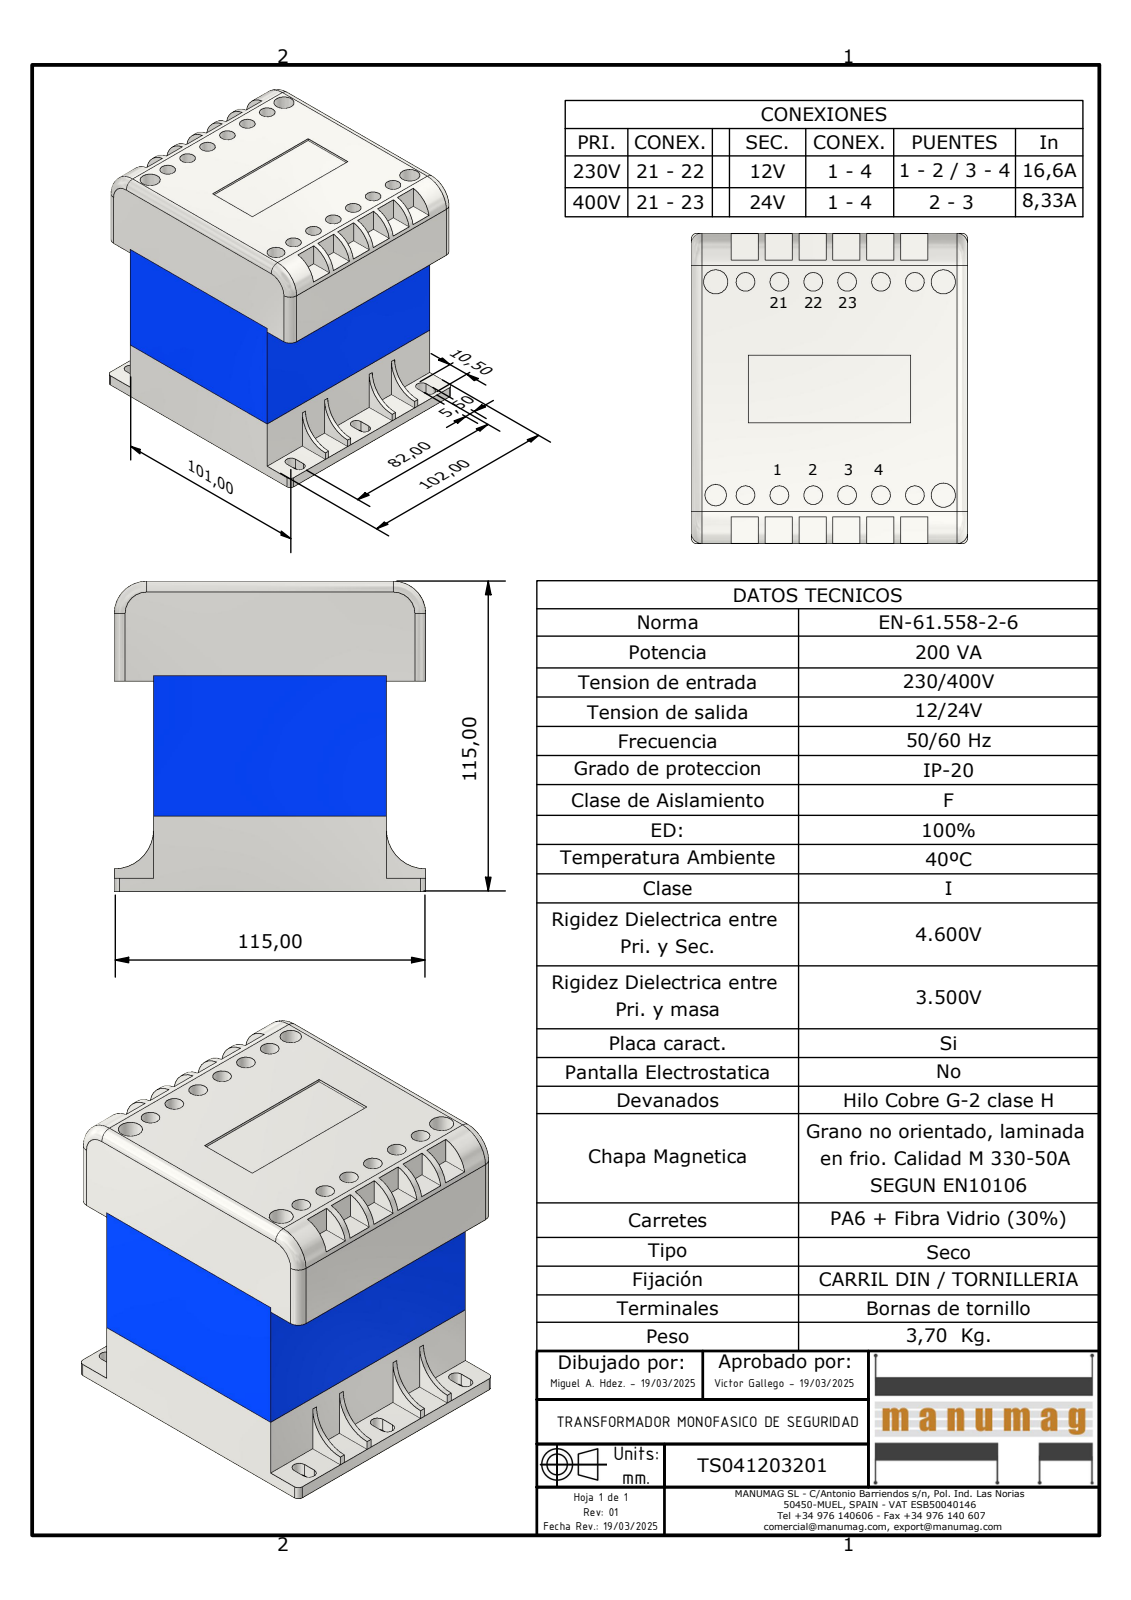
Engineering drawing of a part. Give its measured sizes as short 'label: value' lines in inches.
name: TS041203201; INFERIOR EI96; CENTRAL EI96-50; SUPERIOR EI96
written by: Autodesk Inventor 2023 (AUTOMOTIVE_DESIGN)
unit: in
bodies: 11 solids, 200 faces (152 planar, 44 cylindrical, 4 other)
size: 4.528 × 4.528 × 4.016
volume: 29.25 in³; area: 199.5 in²
holes: 12× ⌀0.276, 3× ⌀0.354, 1× ⌀0.315
rounds: 8× R0.098, 6× R0.157, 4× R0.079, 2× R0.472, 2× R0.571
face distances: 0.039, 3.346, 3.976, 0.197, 4.016, 3.15, 4.528, 2.953, 3.386, 3.937
hole spacings: 0.492, 3.149, 0.984, 3.11, 3.262, 1.476, 3.443, 1.969
